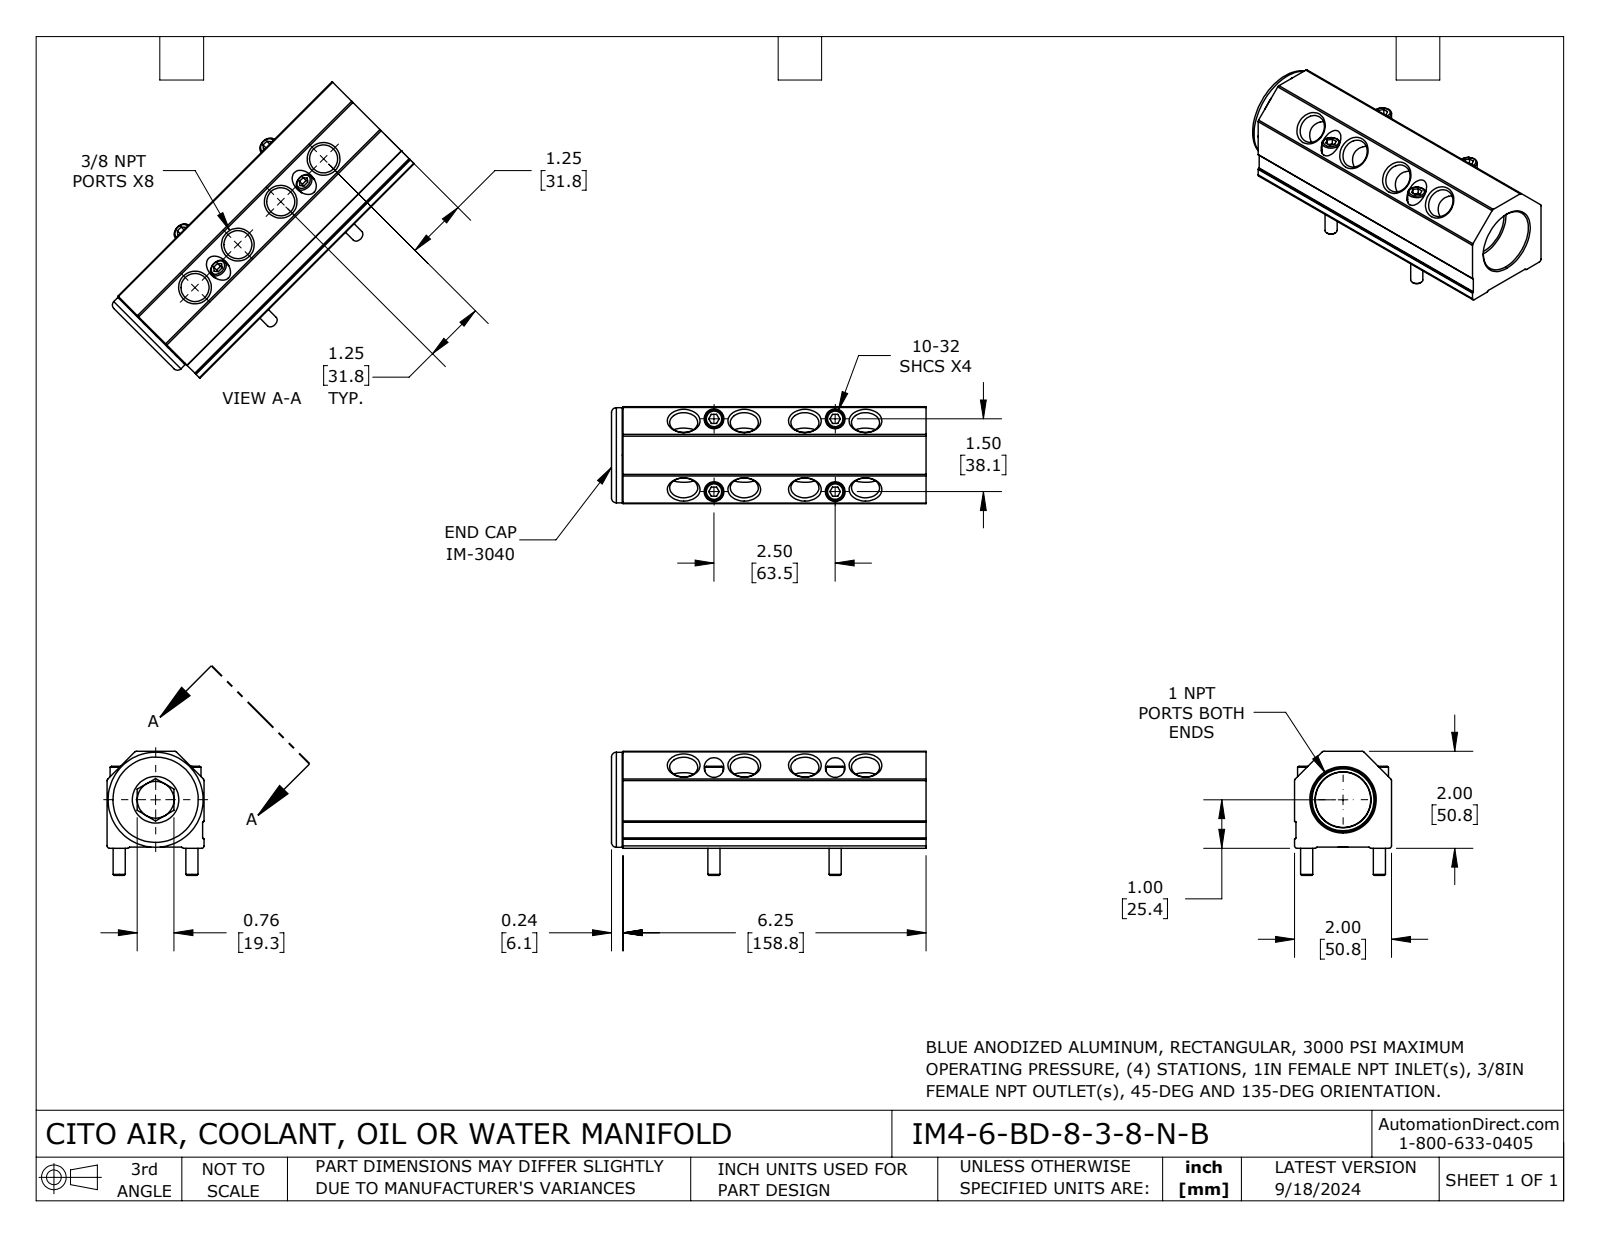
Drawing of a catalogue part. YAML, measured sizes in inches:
part_name: "IM4-6-BD-8-3-8-N-B"
step_written_by: "SolidWorks 2023 (CONFIG_CONTROL_DESIGN)"
units: inches
bodies: {solids: 6, faces: 213, planar: 81, cylindrical: 74, other: 58}
overall_size: [6.49, 2.56, 2]
volume: 15.79
surface_area: 101.7
round_holes:
  - {diameter: 0.578, count: 8}
  - {diameter: 0.266, count: 4}
  - {diameter: 0.406, count: 4}
  - {diameter: 0.758, count: 1}
  - {diameter: 1.156, count: 1}
  - {diameter: 1.637, count: 1}
round_bosses_or_shafts:
  - {diameter: 0.375, count: 4}
  - {diameter: 0.25, count: 4}
  - {diameter: 1.96, count: 1}
  - {diameter: 1.359, count: 1}
  - {diameter: 1.293, count: 1}
  - {diameter: 1.14, count: 1}
partial_cylinders:
  - {radius: 0.05, count: 8}
  - {radius: 0.01, count: 4}
face_to_face_distances: [2, 1.975, 0.025, 6.25, 0.028, 1.972, 0.24, 6.49, 0.764, 0.524]
hole_center_spacings: [1.25, 2.5, 1.5, 2.915, 3.75]
